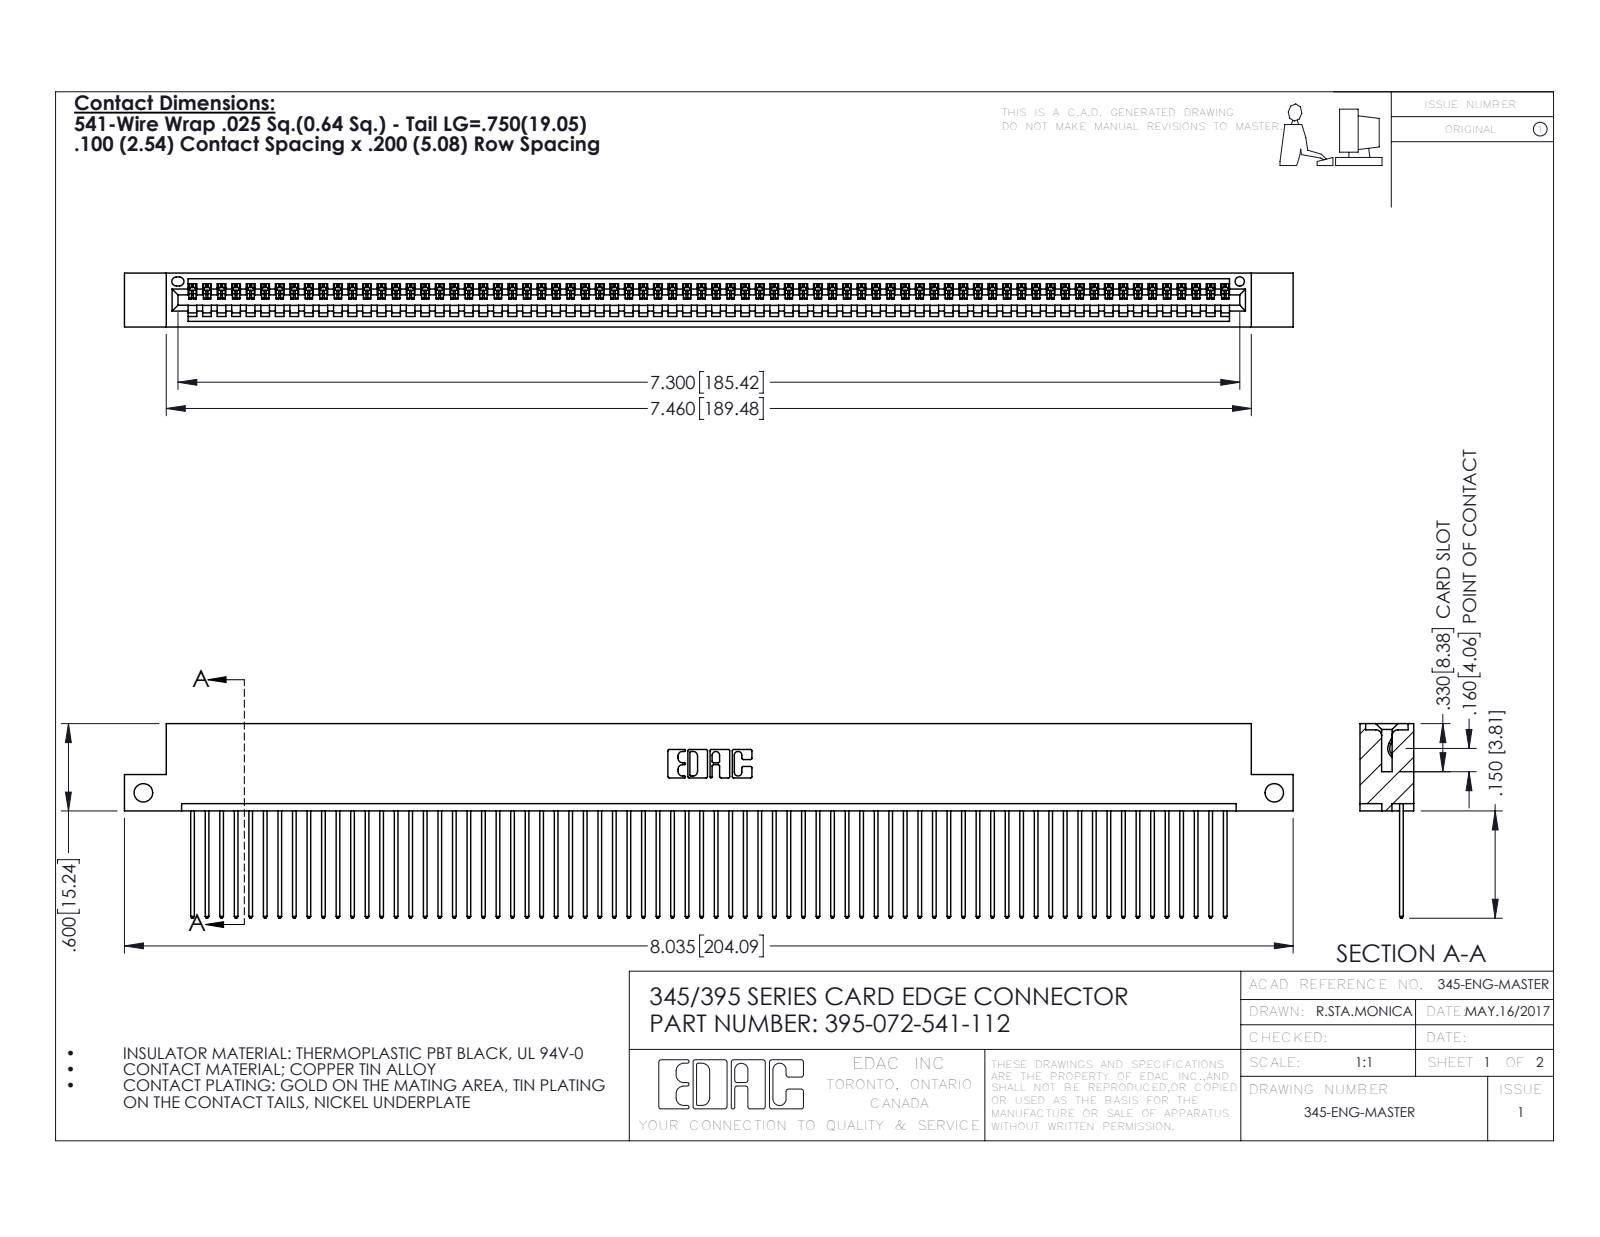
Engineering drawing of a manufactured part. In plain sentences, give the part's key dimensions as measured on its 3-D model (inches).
The part is named "345 Part_Flush Mounting Lugs - Side Mount; 345-292-001_345-293-141; 395-072-541-112". Its 3-D file was written by "SolidWorks 2016 (CONFIG_CONTROL_DESIGN)". It is 73 solids with 4302 faces: 2960 planar, 1342 cylindrical and 0 other. Overall it measures 8.035 by 1.337 by 0.37 inches. Its volume is 1.207 cubic inches and its surface area 43.32 square inches. Round holes: 2 of diameter 0.128, 1 of diameter 0.064. Partial cylindrical surfaces (rounded edges, fillets, slot ends): 144 of radius 0.006, 144 of radius 0.01, 22 of radius 0.01, 6 of radius 0.007, 6 of radius 0.031, 3 of radius 0.026, 2 of radius 0.031, 2 of radius 0.04. The main face-to-face distances are 0.072, 0.298, 0.098, 0.272, 0.025, 0.37, 0.2, 0.225, 0.149, 0.072. The hole center spacings are 7.775.
